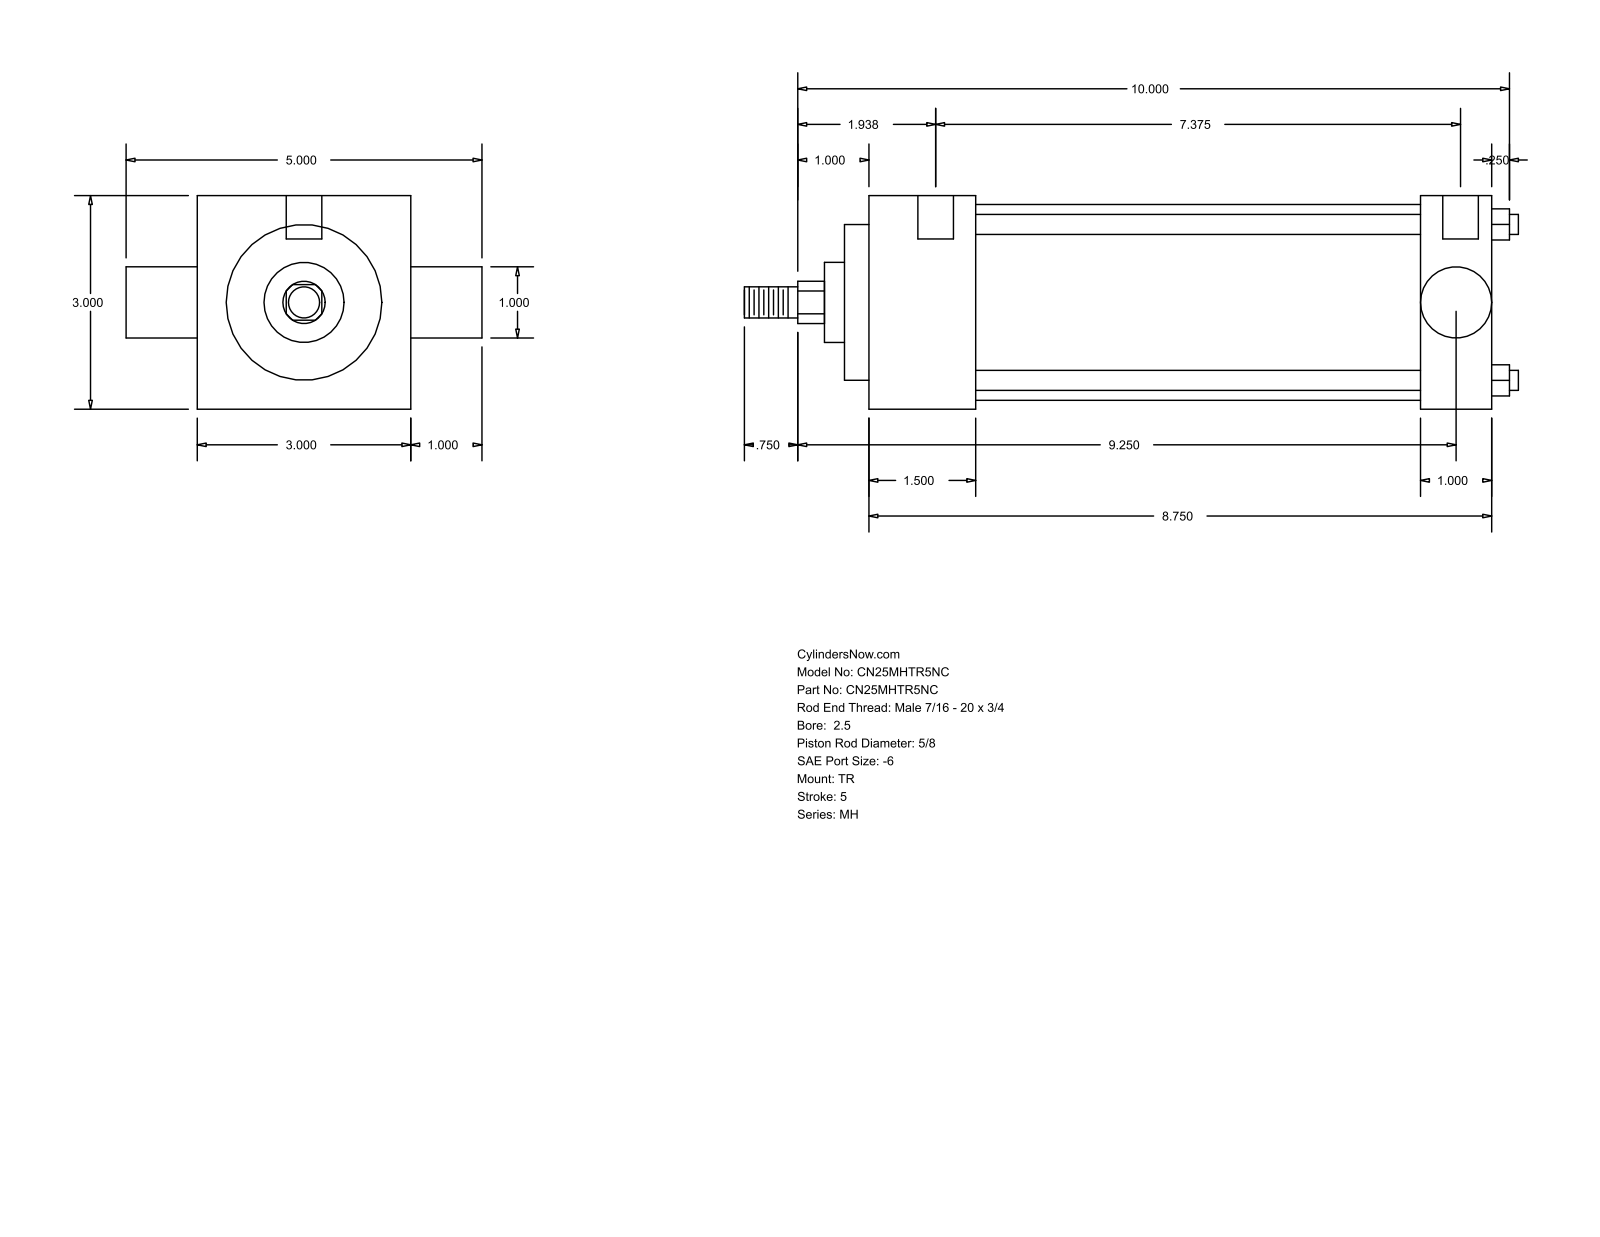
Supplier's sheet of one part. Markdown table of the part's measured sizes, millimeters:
| quantity | value |
| --- | --- |
| part name | MH_TR__0250_0.625 |
| STEP written by | GSSL Pune (CONFIG_CONTROL_DESIGN) |
| units | millimeters |
| bodies | 0 solids, 86 faces (61 planar, 25 cylindrical, 0 other) |
| overall size | 276.23 × 127 × 76.2 |
| round holes (diameter × count) | 5.56 × 3, 12.7 × 2 |
| round bosses / shafts (diameter × count) | 7.14 × 4, 69.85 × 1, 55.55 × 1, 28.57 × 1, 25.35 × 1, 15.88 × 1, 11.11 × 1 |
| partial cylindrical surfaces (radius × count) | 7.54 × 1 |
| main face-to-face distances | 76.2, 222.25, 25.4, 38.1, 184.15, 196.85, 158.75, 8.73, 46.83, 205.58 |
| hole center spacings | 3.17, 4.76, 187.33, 190.5, 192.09, 195.26 |
